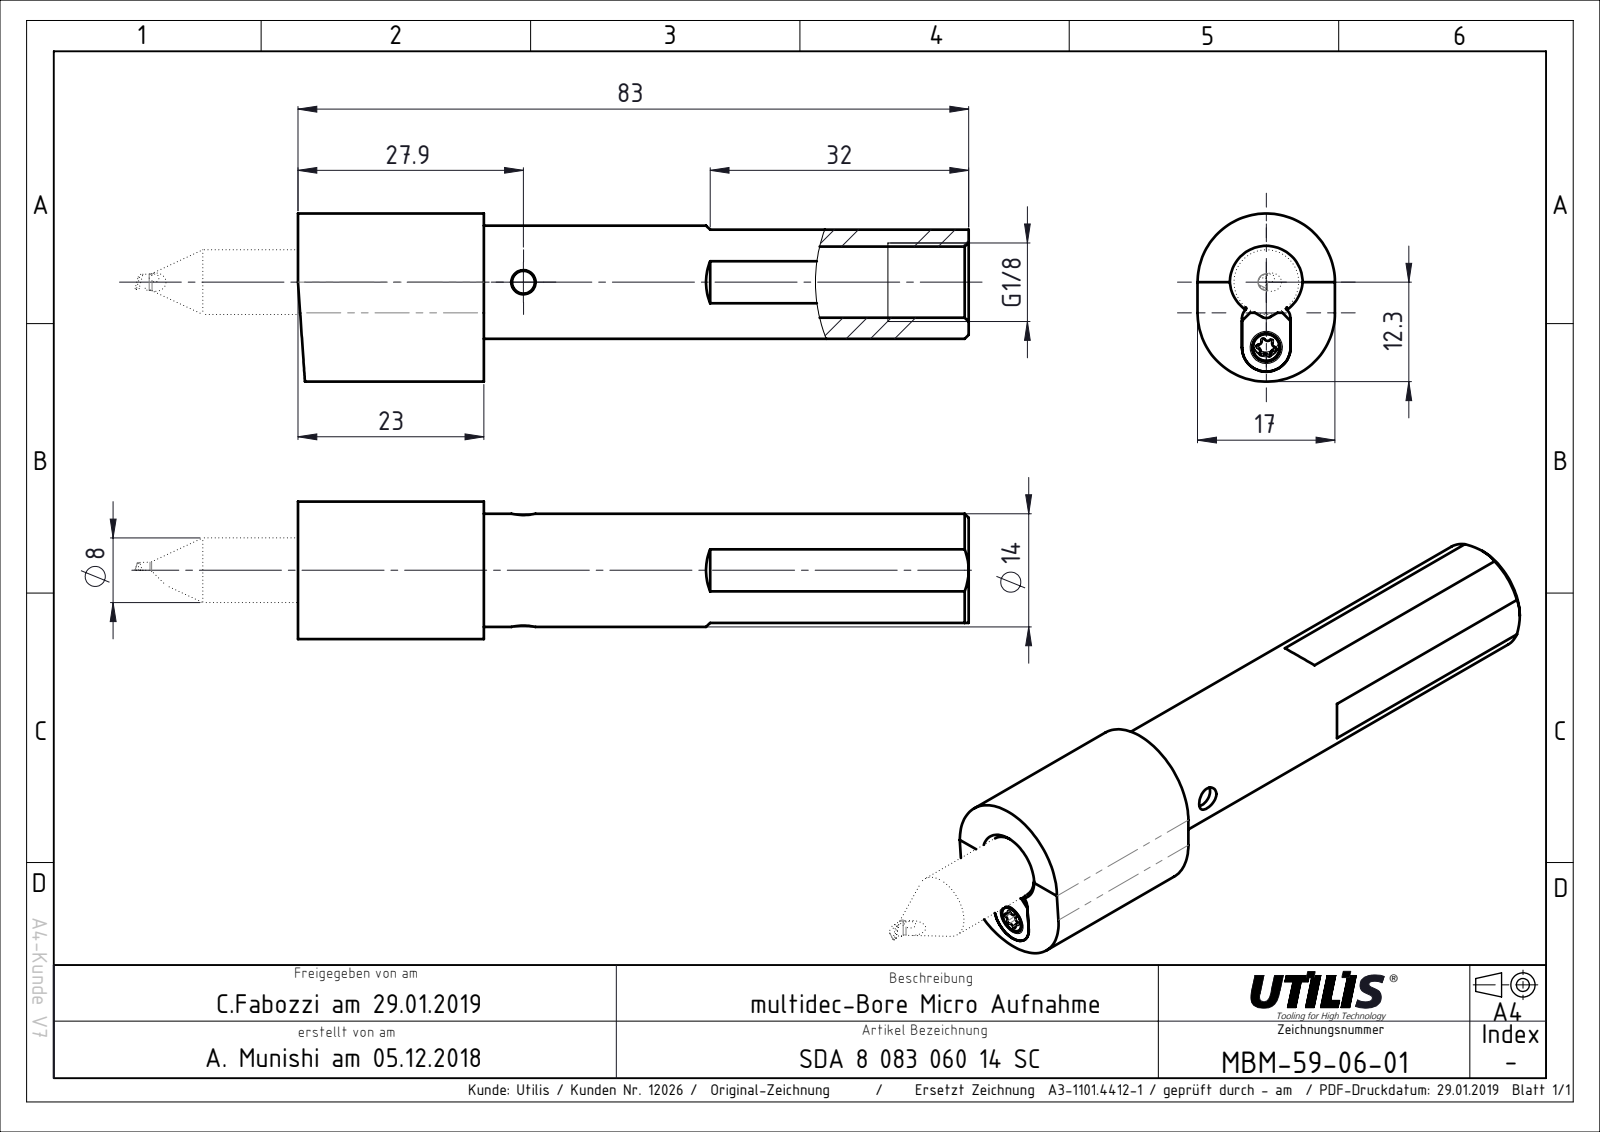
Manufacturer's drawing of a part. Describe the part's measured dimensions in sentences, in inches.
The part is named "MBM-59-06-01". Its 3-D file was written by "SolidWorks 2018 (CONFIG_CONTROL_DESIGN)". It is 1 solid with 45 faces: 13 planar, 16 cylindrical and 16 other. Overall it measures 3.268 by 0.819 by 0.669 inches. Its volume is 0.641 cubic inches and its surface area 10.76 square inches. Round holes: 1 of diameter 0.118, 1 of diameter 0.13, 1 of diameter 0.315, 1 of diameter 0.346. Round bosses or shafts: 1 of diameter 0.551. Partial cylindrical surfaces (rounded edges, fillets, slot ends): 2 of radius 0.335, 1 of radius 0.118. The main face-to-face distances are 0.079, 0.591, 0.669, 0.906, 0.217, 0.453, 3.268, 2.362, 0.138, 0.236.
